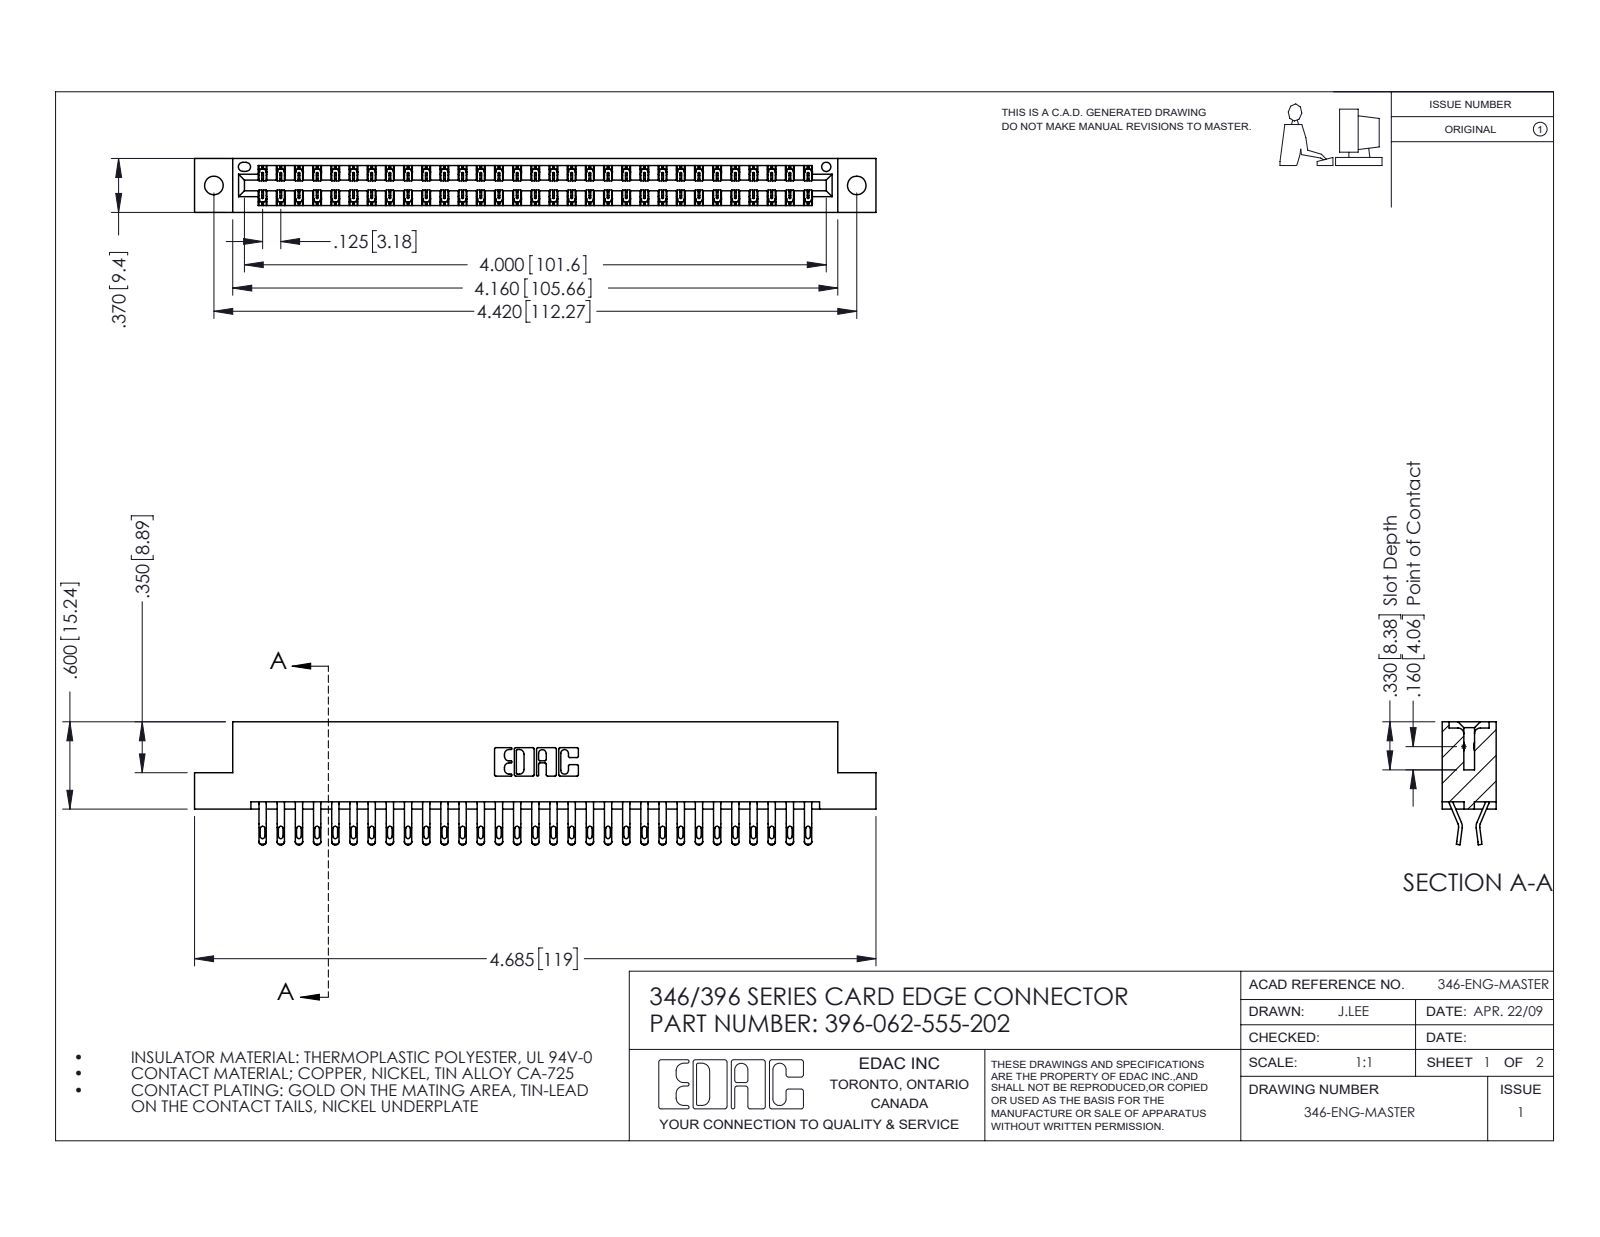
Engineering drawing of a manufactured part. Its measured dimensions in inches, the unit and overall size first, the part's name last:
Units: inches
Overall size (bounding box): 4.685 × 0.845 × 0.37
Round holes (diameter × count): ⌀0.128 ×2, ⌀0.064 ×1
Partial cylindrical surfaces — rounded edges, fillets, slot ends (radius × count): R0.016 ×124, R0.02 ×124, R0.006 ×93, R0.01 ×22, R0.007 ×6, R0.031 ×6, R0.026 ×3, R0.01 ×2
Main face-to-face distances: 0.048, 0.322, 0.37, 0.25, 0.025, 0.072, 0.298, 0.275, 0.148, 0.222
Hole centre spacings: 0.246, 4.212, 4.42
Volume: 0.712 in³ · Surface area: 25.15 in²
Bodies: 63 solids, 3718 faces (2122 planar, 1596 cylindrical, 0 other)
Part name (STEP PRODUCT): 346 Part_Flush Mounting Lugs - 0.128 Dia; 396-062-555-202; 345-292-001_555 Tail
STEP written by: SolidWorks 2016 (CONFIG_CONTROL_DESIGN)
